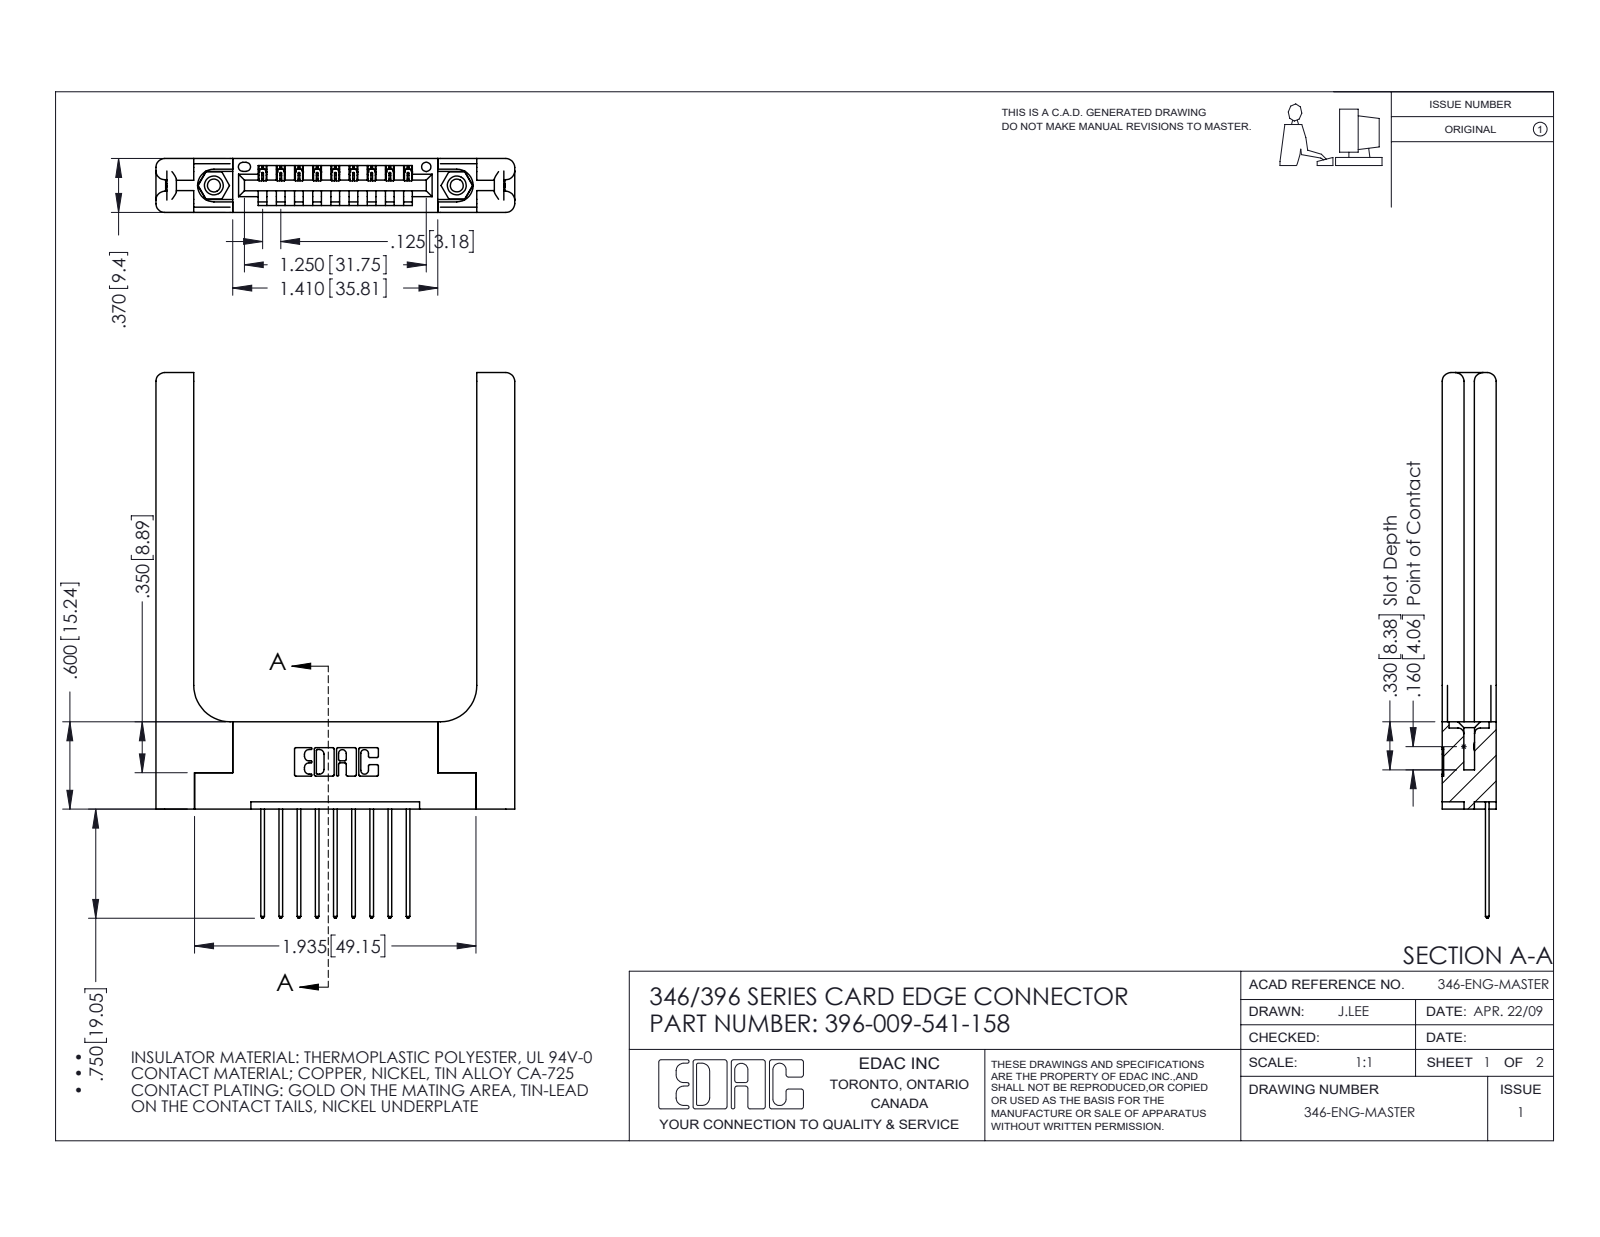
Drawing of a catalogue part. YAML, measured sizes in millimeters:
part_name: "345-292-001_345-293-141; 345-250-001_345-250-001-102; 346-220-058_345-220-058; 346 Part_Flush Mounting Lugs - 0.156 Dia-TH (+1 more)"
step_written_by: "SolidWorks 2016 (CONFIG_CONTROL_DESIGN)"
units: millimeters
bodies: {solids: 14, faces: 900, planar: 584, cylindrical: 256, other: 60}
overall_size: [95.3, 62.6, 9.4]
volume: 13300
surface_area: 12240
round_holes:
  - {diameter: 2.3, count: 2}
  - {diameter: 3.2, count: 2}
  - {diameter: 4, count: 2}
  - {diameter: 1.6, count: 1}
round_bosses_or_shafts:
  - {diameter: 3.9, count: 2}
partial_cylinders:
  - {radius: 0.3, count: 22}
  - {radius: 0.2, count: 18}
  - {radius: 0.3, count: 18}
  - {radius: 1.5, count: 16}
  - {radius: 0.2, count: 6}
  - {radius: 0.8, count: 6}
  - {radius: 0.7, count: 3}
  - {radius: 0.8, count: 2}
face_to_face_distances: [9.4, 3.8, 1.8, 3.8, 5.6, 1.2, 8.2, 6.4, 2.6, 4.4]
hole_center_spacings: [6.2, 37.2, 42.4]
